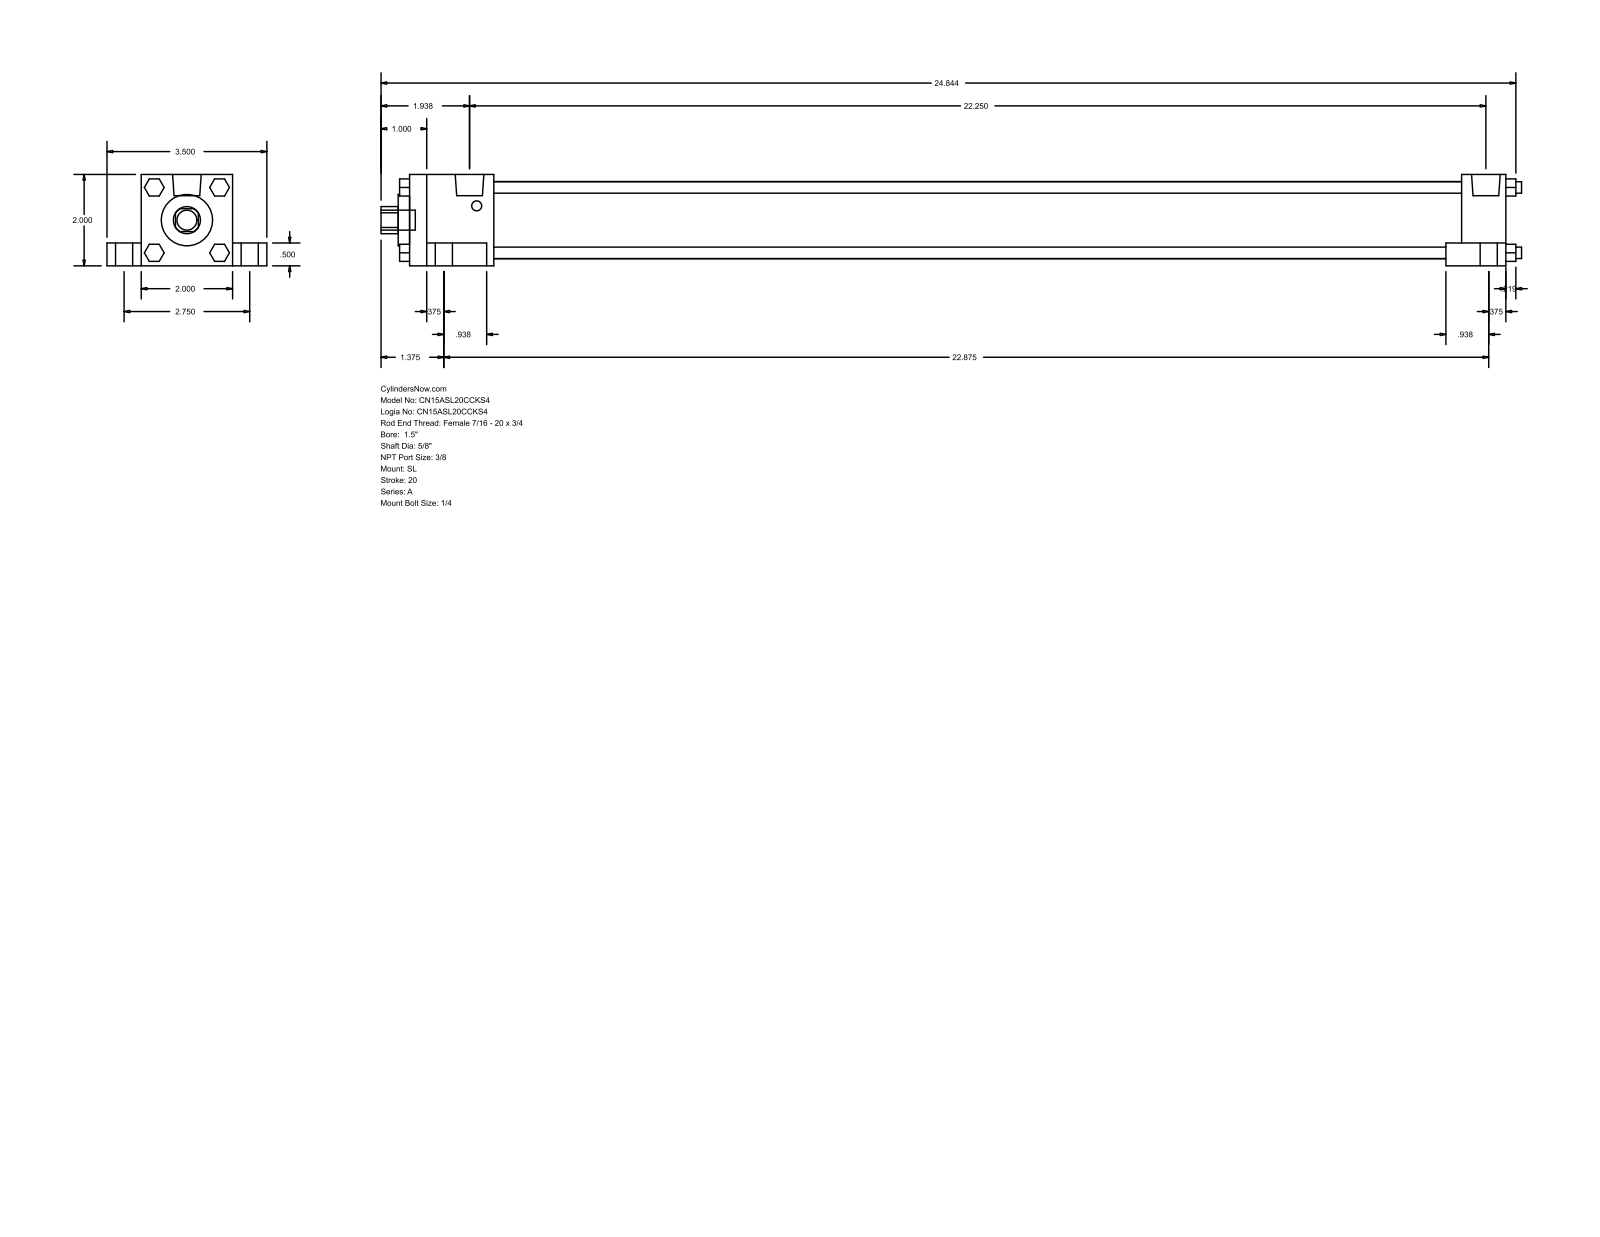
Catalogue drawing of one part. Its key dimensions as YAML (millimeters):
part_name: "A_SL__0150_0.625"
step_written_by: "GSSL Pune (CONFIG_CONTROL_DESIGN)"
units: millimeters
bodies: {solids: 0, faces: 148, planar: 112, cylindrical: 36, other: 0}
overall_size: [634.21, 88.9, 50.8]
round_holes:
  - {diameter: 15.88, count: 1}
  - {diameter: 28.57, count: 1}
  - {diameter: 42.93, count: 1}
round_bosses_or_shafts:
  - {diameter: 15.88, count: 4}
  - {diameter: 9.53, count: 4}
  - {diameter: 6.35, count: 4}
  - {diameter: 5.56, count: 4}
  - {diameter: 15.93, count: 2}
  - {diameter: 11.11, count: 1}
partial_cylinders:
  - {radius: 7.54, count: 1}
face_to_face_distances: [50.8, 19.05, 12.7, 38.1, 69.85, 609.6, 9.52, 33.34, 584.99, 24.61]
